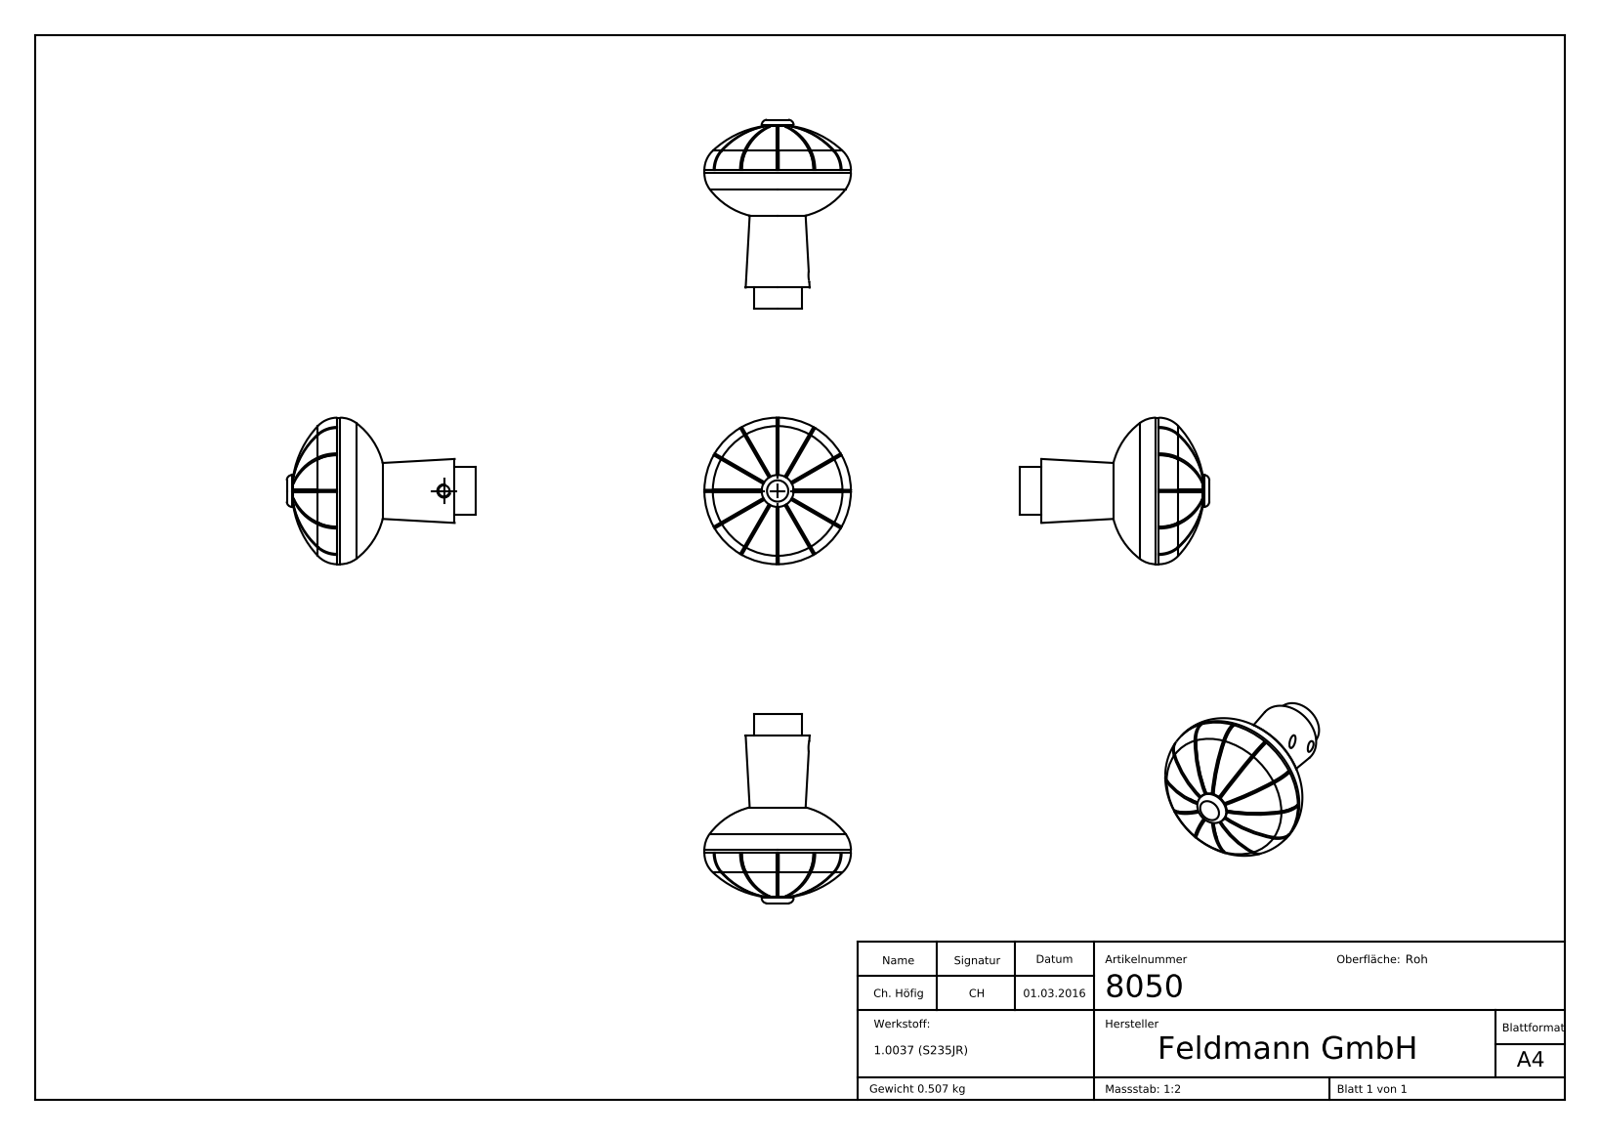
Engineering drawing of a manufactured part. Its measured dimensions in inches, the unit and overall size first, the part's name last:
Units: inches
Overall size (bounding box): 2.795 × 2.165 × 2.165
Round holes (diameter × count): ⌀0.165 ×1
Round bosses / shafts (diameter × count): ⌀2.165 ×1, ⌀0.709 ×1, ⌀0.472 ×1
Main face-to-face distances: 0.319, 0.315, 1.575, 1.26, 2.795, 2.48, 1.22, 2.05, 1.735, 0.476
Volume: 3.963 in³ · Surface area: 17.58 in²
Bodies: 1 solid, 290 faces (111 planar, 8 cylindrical, 171 other)
Part name (STEP PRODUCT): 8050
STEP written by: SolidWorks 2015 (CONFIG_CONTROL_DESIGN)
